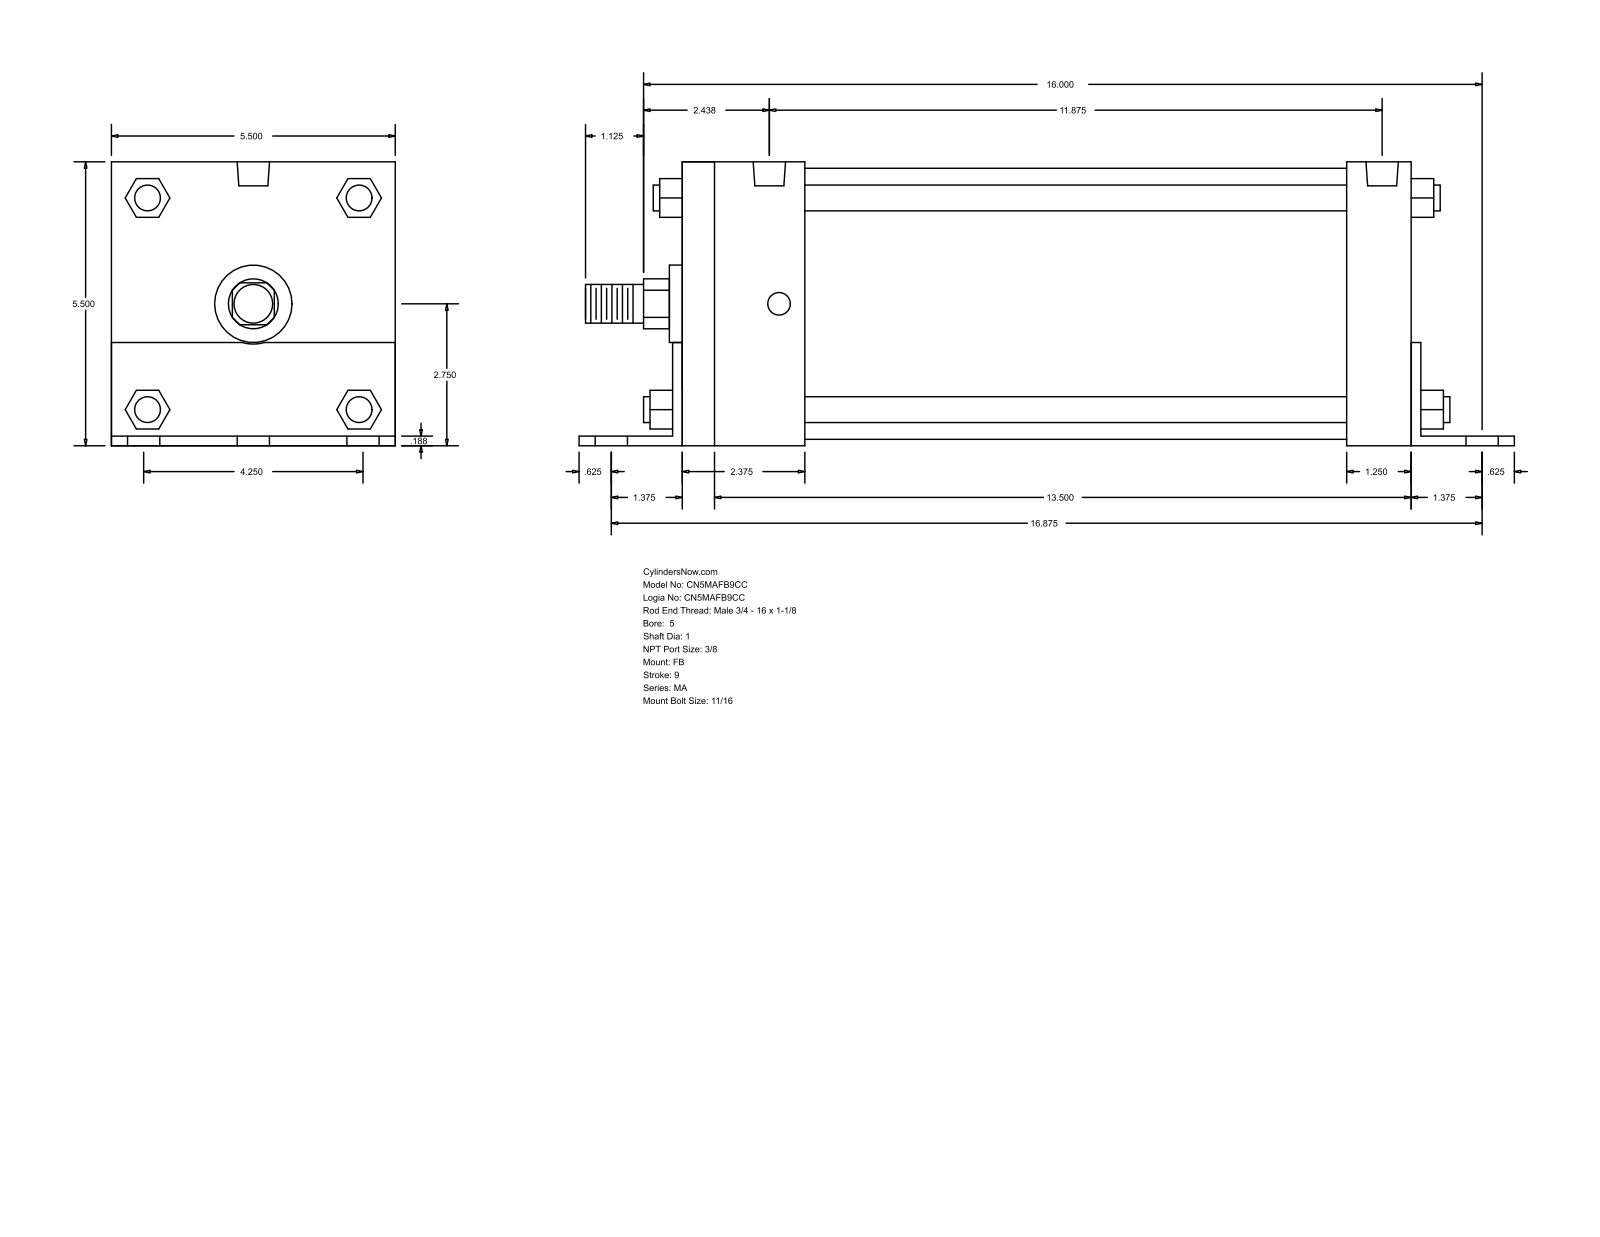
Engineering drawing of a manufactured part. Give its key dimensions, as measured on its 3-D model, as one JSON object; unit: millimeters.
{"part_name": "MA_FB__0500_1", "step_written_by": "GSSL Pune (CONFIG_CONTROL_DESIGN)", "units": "millimeters", "bodies": {"solids": 0, "faces": 140, "planar": 105, "cylindrical": 35, "other": 0}, "overall_size": [460.38, 139.75, 139.7], "round_holes": [[17.46, 6], [11.11, 4], [15.93, 2]], "round_bosses_or_shafts": [[12.7, 4], [133.35, 1], [38.1, 1], [25.4, 1], [19.05, 1]], "partial_cylinders_radius": [[12.29, 1], [19.81, 1]], "face_to_face_distances": [139.7, 4.76, 139.75, 4.71, 134.99, 358.77, 4.77, 363.54, 363.53, 368.3], "hole_center_spacings": [53.98, 432.02, 428.63, 73.04, 76.34, 94.68, 98.63, 107.96]}
